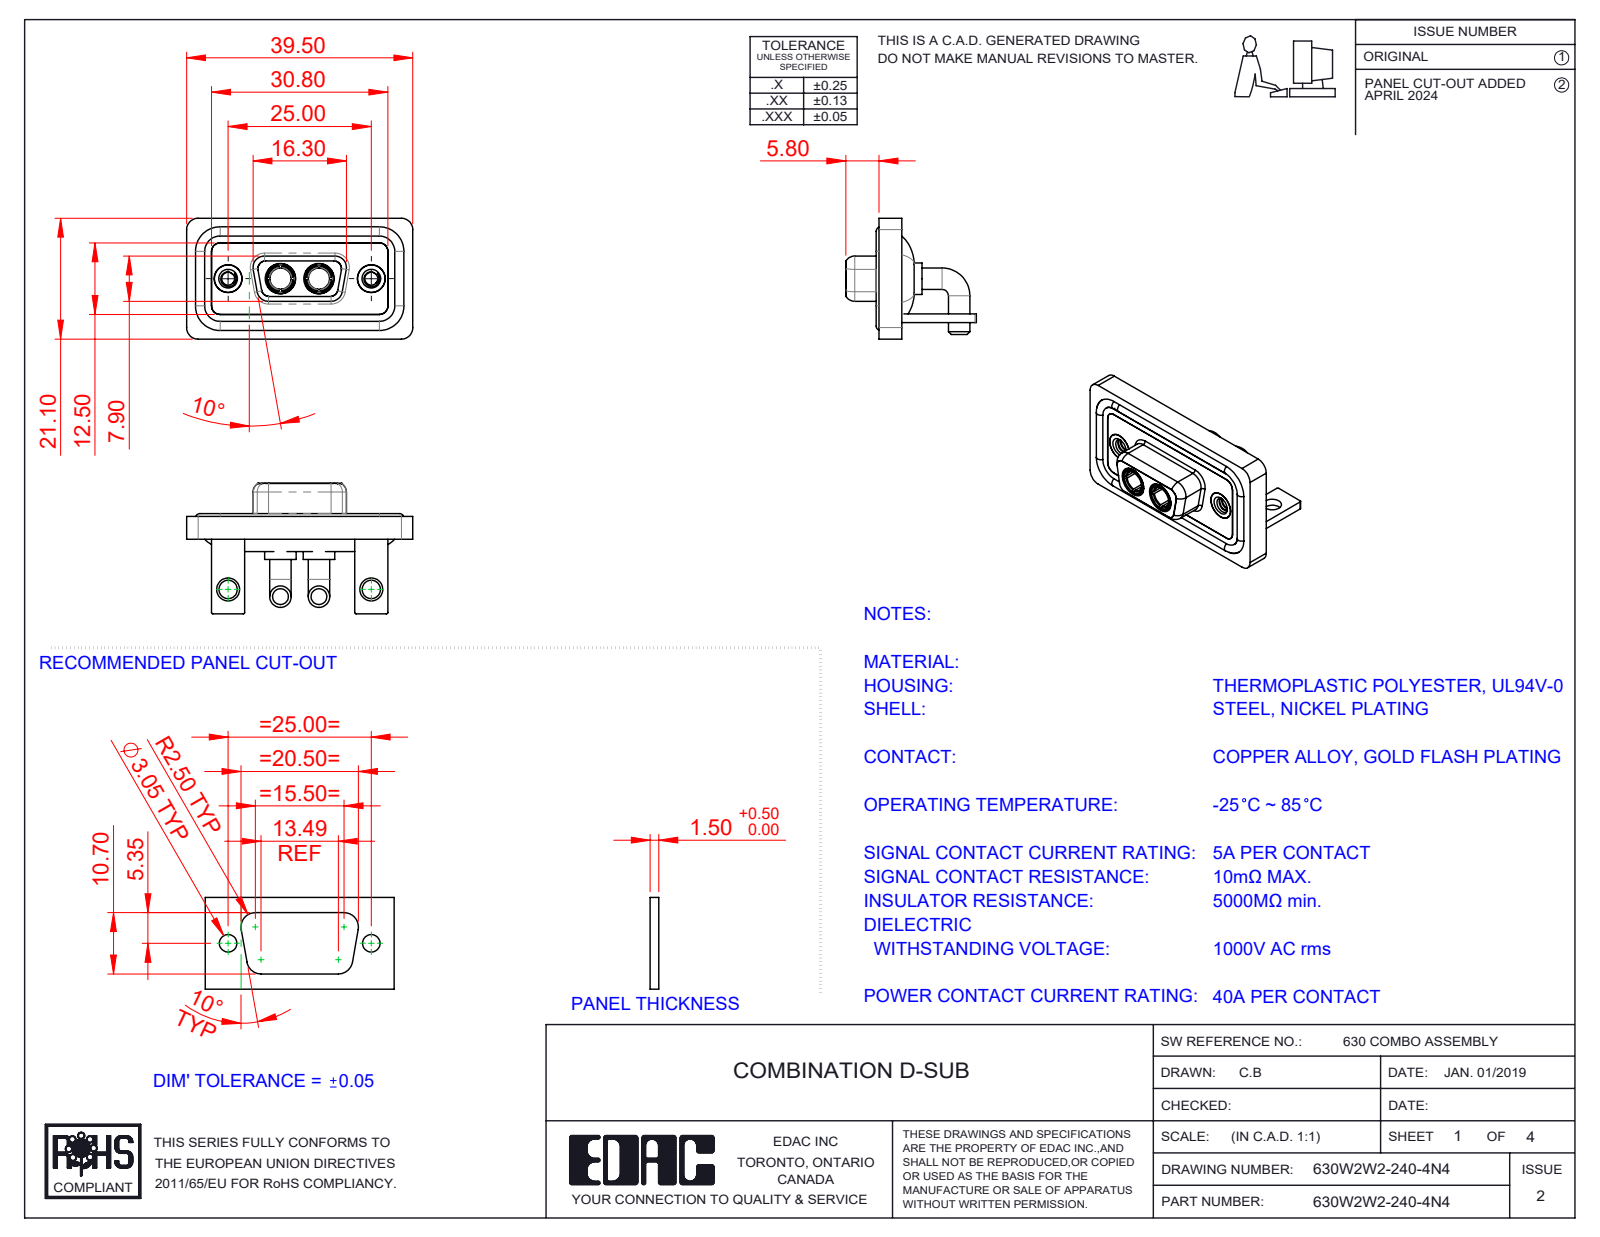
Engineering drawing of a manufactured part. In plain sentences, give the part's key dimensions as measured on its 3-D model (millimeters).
The part is named "630W2W2-140-4N4; 630Combo Housing_2W2; 630Combo Waterproof Housing_09 Contacts; 630Combo Shell Front_09 Contacts (+4 more)". Its 3-D file was written by "SolidWorks 2023 (CONFIG_CONTROL_DESIGN)". It is 13 solids with 590 faces: 183 planar, 262 cylindrical and 145 other. Overall it measures 39.5 by 22.8 by 21.1 millimeters. Its volume is 5 328 cubic millimeters and its surface area 8 609 square millimeters. Round holes: 4 of diameter 4.85, 2 of diameter 2.26, 2 of diameter 3.2, 2 of diameter 3.7, 2 of diameter 4, 2 of diameter 4.05, 2 of diameter 5, 2 of diameter 5.3. Round bosses or shafts: 4 of diameter 3.75, 4 of diameter 1.6, 2 of diameter 5.5, 2 of diameter 5.2, 2 of diameter 4.96, 2 of diameter 4.95, 2 of diameter 4.8, 2 of diameter 4.75. Partial cylindrical surfaces (rounded edges, fillets, slot ends): 19 of radius 2, 18 of radius 1.5, 16 of radius 0.25, 8 of radius 1.35, 8 of radius 1.6, 5 of radius 0.5, 4 of radius 0.6, 4 of radius 0.65. The main face-to-face distances are 0.4, 2.9, 1.5, 1.8, 1.1, 3.7, 0.8, 2.5, 1.6, 3.1. The hole center spacings are 9.14, 15.86, 25, 6.72.
